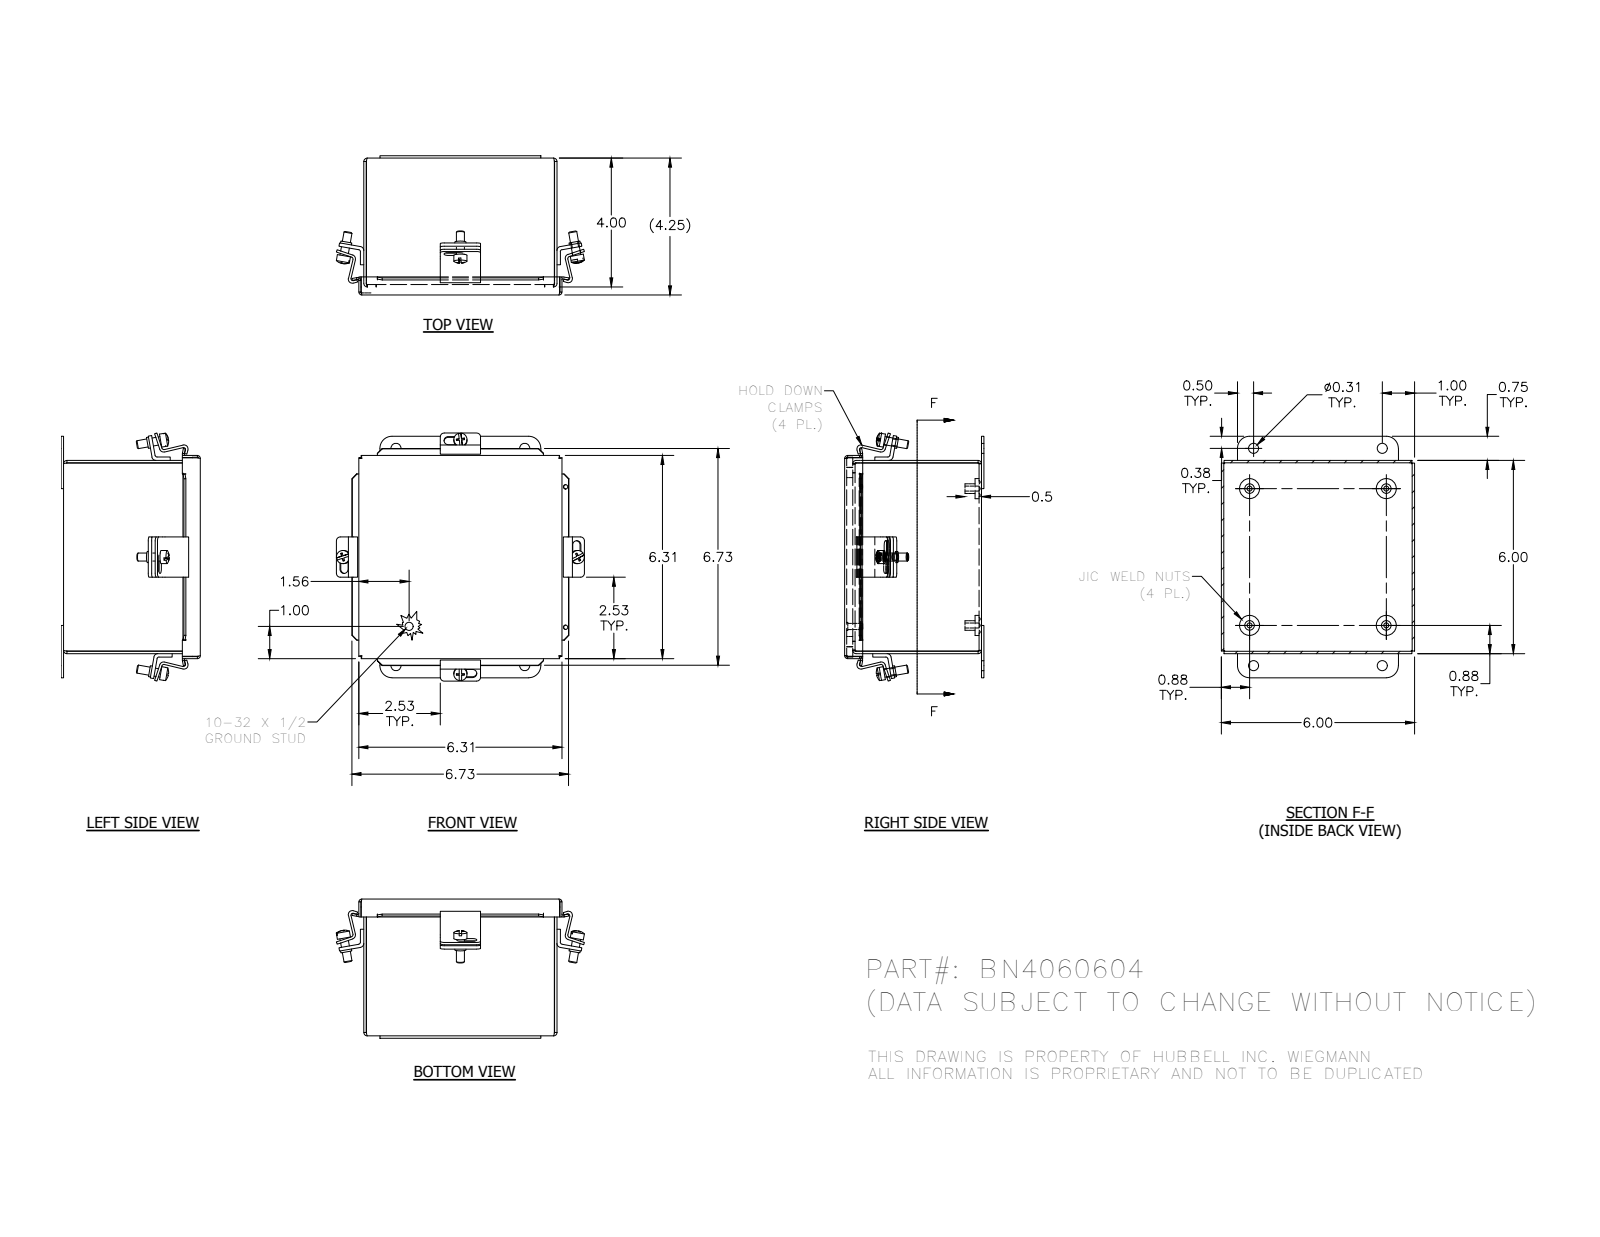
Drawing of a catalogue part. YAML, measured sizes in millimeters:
part_name: "C2002_1; BN40606LID_1; 38811_1; 316161_1 (+6 more)"
step_written_by: "SolidWorks 2014 (AUTOMOTIVE_DESIGN)"
units: millimeters
bodies: {solids: 23, faces: 537, planar: 295, cylindrical: 172, other: 70}
overall_size: [195.7, 195.7, 109.8]
volume: 306400
surface_area: 319000
round_holes:
  - {diameter: 4, count: 4}
  - {diameter: 5, count: 4}
  - {diameter: 7.9, count: 4}
  - {diameter: 3.5, count: 2}
round_bosses_or_shafts:
  - {diameter: 6.4, count: 5}
  - {diameter: 15.9, count: 4}
  - {diameter: 10.4, count: 4}
  - {diameter: 8.7, count: 4}
  - {diameter: 7.6, count: 4}
  - {diameter: 4.8, count: 1}
partial_cylinders:
  - {radius: 0.8, count: 16}
  - {radius: 3.2, count: 16}
  - {radius: 1.6, count: 12}
  - {radius: 3.2, count: 12}
  - {radius: 2.4, count: 8}
  - {radius: 2.7, count: 8}
  - {radius: 3.4, count: 8}
  - {radius: 9.5, count: 4}
face_to_face_distances: [1.9, 150.5, 106.3, 1.6, 152.4, 148.6, 108, 104.5, 106.1, 99.7]
hole_center_spacings: [31.9, 108, 109.5, 139.8, 101.6, 152.7, 171.5, 174.6]
